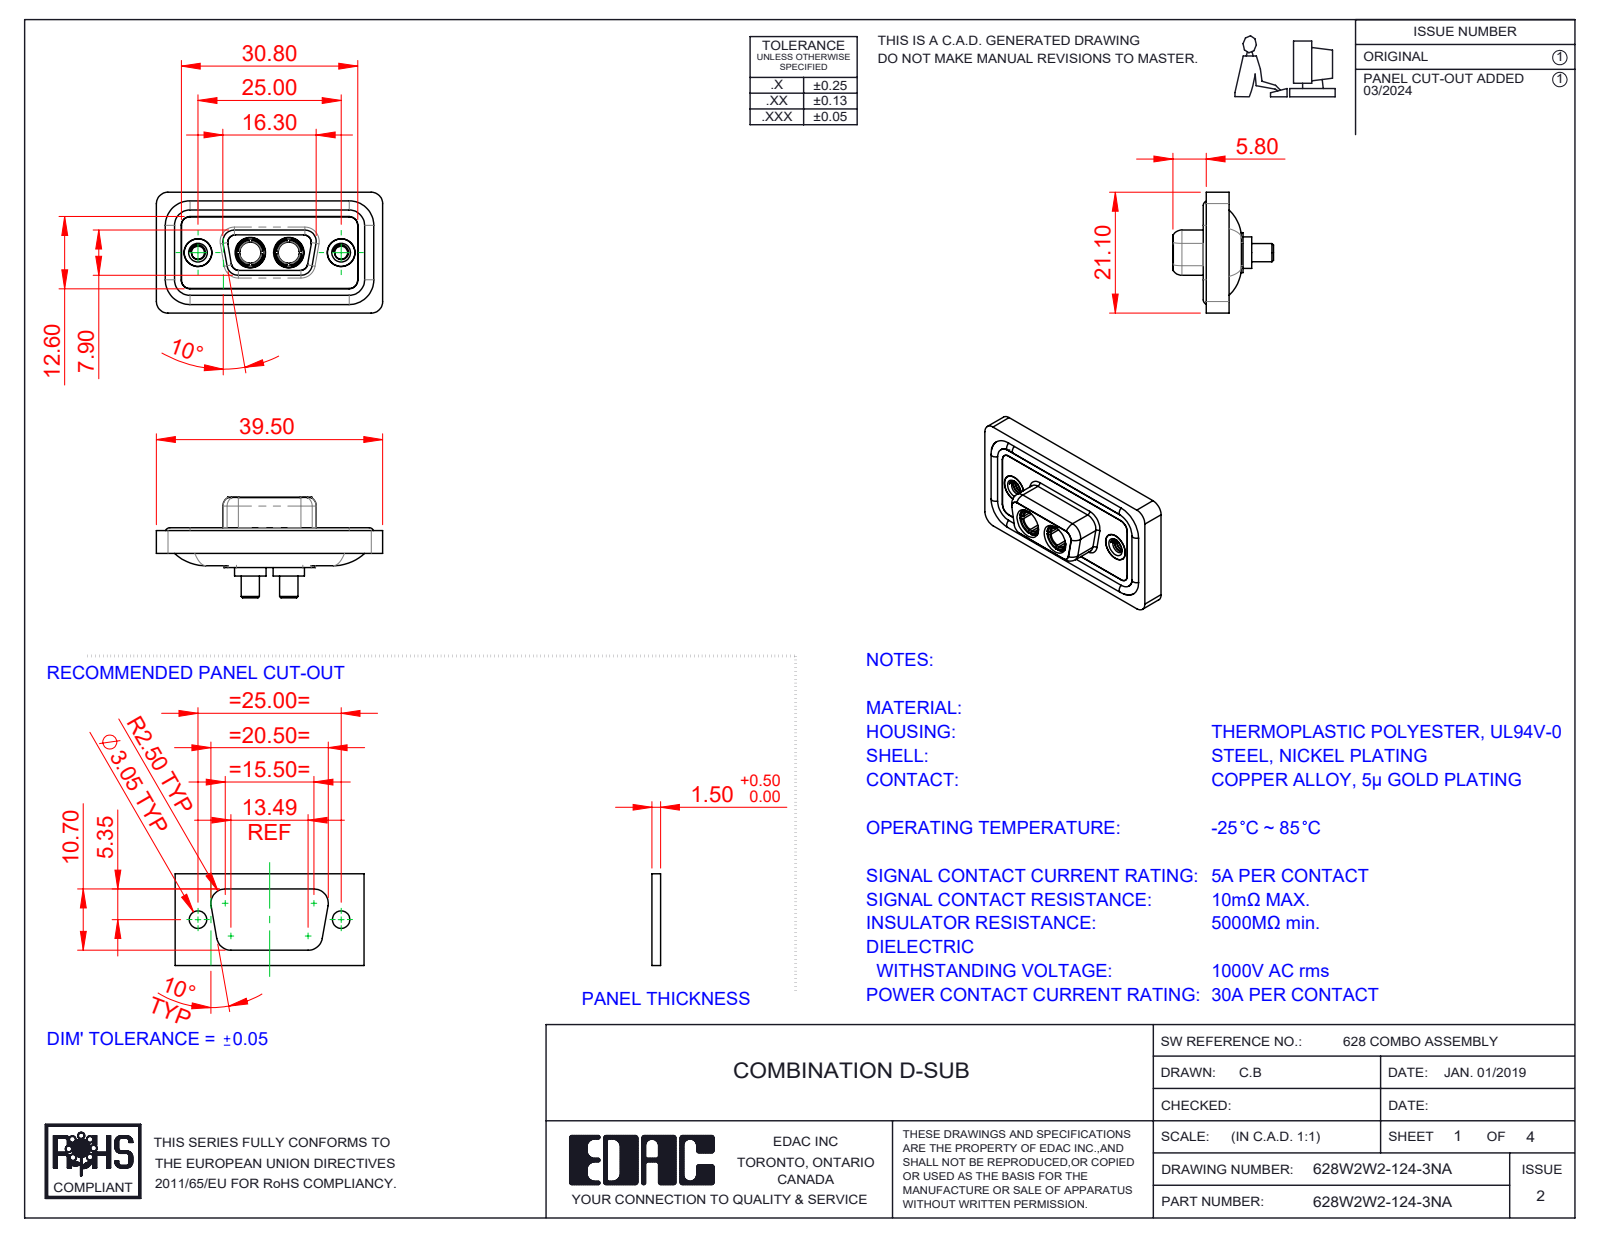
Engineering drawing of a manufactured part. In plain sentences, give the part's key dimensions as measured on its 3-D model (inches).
The part is named "628W2W2-124-3NA; 628Combo Waterproof Housing_09 Contacts; 628Combo Shell Front_09 Contacts; 628Combo Shell Rear_09 Contacts (+3 more)". Its 3-D file was written by "SolidWorks 2023 (CONFIG_CONTROL_DESIGN)". It is 11 solids with 532 faces: 163 planar, 236 cylindrical and 133 other. Overall it measures 1.555 by 0.831 by 0.691 inches. Its volume is 0.289 cubic inches and its surface area 11.85 square inches. Round holes: 4 of diameter 0.191, 2 of diameter 0.089, 2 of diameter 0.146, 2 of diameter 0.157, 2 of diameter 0.159, 2 of diameter 0.197, 2 of diameter 0.209. Round bosses or shafts: 4 of diameter 0.063, 2 of diameter 0.217, 2 of diameter 0.205, 2 of diameter 0.195, 2 of diameter 0.195, 2 of diameter 0.189, 2 of diameter 0.187, 2 of diameter 0.148. Partial cylindrical surfaces (rounded edges, fillets, slot ends): 22 of radius 0.059, 18 of radius 0.079, 8 of radius 0.053, 8 of radius 0.063, 4 of radius 0.01, 4 of radius 0.02, 4 of radius 0.024, 4 of radius 0.026. The main face-to-face distances are 0.016, 0.071, 0.043, 0.114, 0.02, 0.063, 0.222, 0.293, 0.059, 0.211. The hole center spacings are 0.36, 0.624, 0.265, 0.984.
